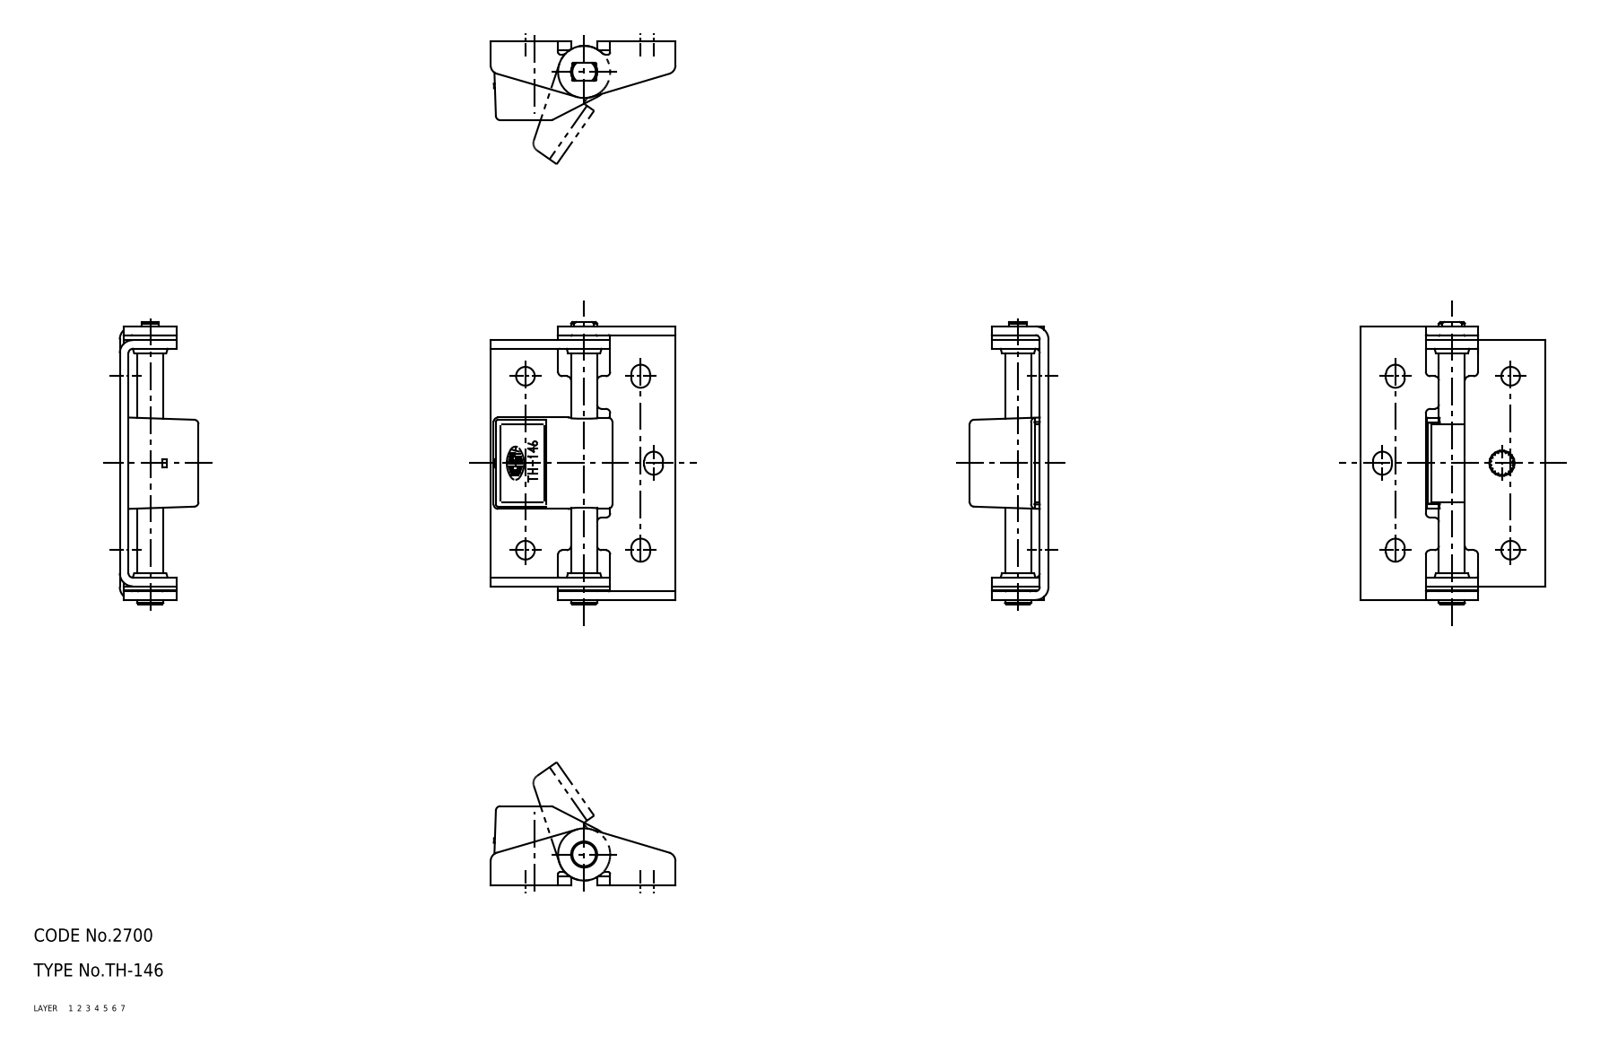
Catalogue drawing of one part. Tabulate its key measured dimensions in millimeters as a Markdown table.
| quantity | value |
| --- | --- |
| part name | 67121172; 67121185; 67121198; 67121211 (+4 more) |
| STEP written by | CADfix (AUTOMOTIVE_DESIGN) |
| units | millimeters |
| bodies | 8 solids, 253 faces (0 planar, 0 cylindrical, 253 other) |
| overall size | 64.9 × 42.5 × 18.1 |
| volume | 10 104 mm³ |
| surface area | 13 763 mm² |
